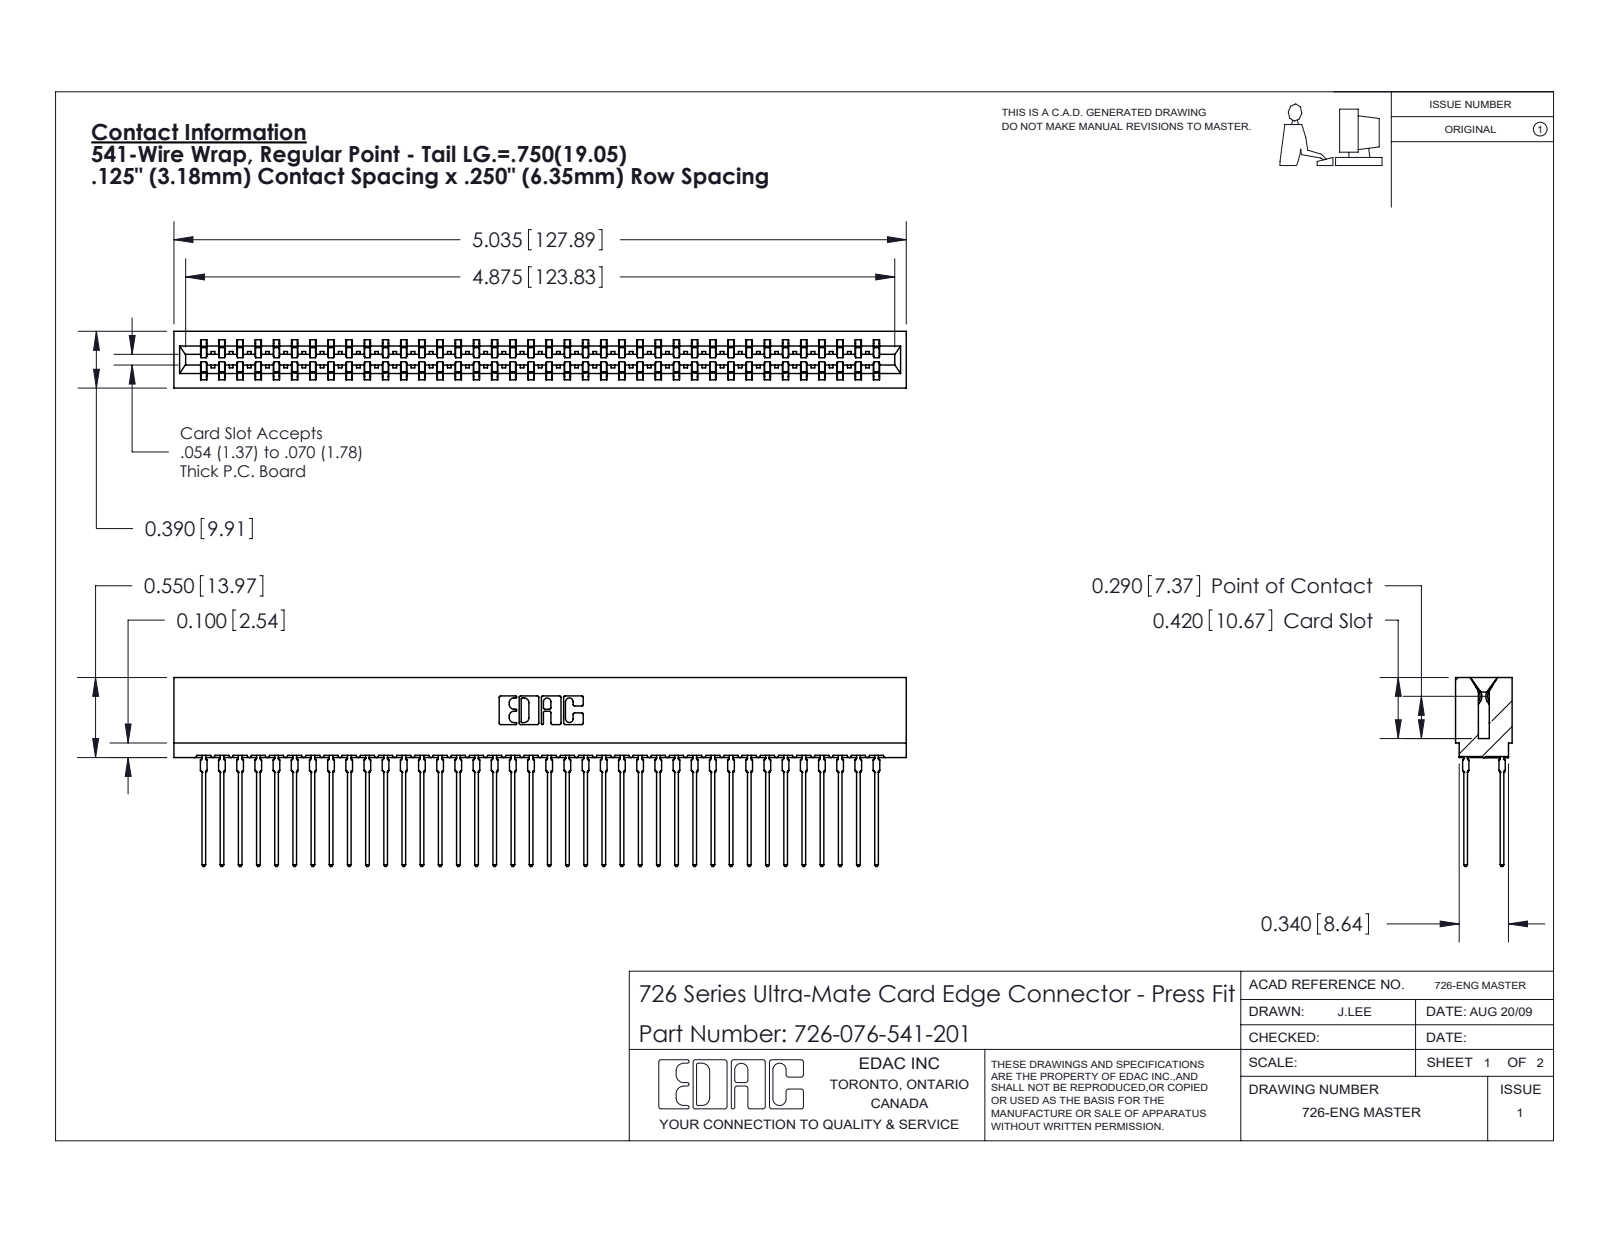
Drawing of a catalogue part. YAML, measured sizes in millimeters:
part_name: "746-292-001_541; 726-076-541-201; 726 Part_.515 Slot Depth - 01"
step_written_by: "SolidWorks 2020 (CONFIG_CONTROL_DESIGN)"
units: millimeters
bodies: {solids: 77, faces: 6899, planar: 3551, cylindrical: 1372, other: 1976}
overall_size: [127.9, 33, 9.9]
volume: 12200
surface_area: 22210
partial_cylinders:
  - {radius: 0.5, count: 152}
  - {radius: 0.4, count: 39}
  - {radius: 0.3, count: 22}
  - {radius: 0.1, count: 8}
  - {radius: 0.3, count: 8}
  - {radius: 0.2, count: 6}
  - {radius: 0.8, count: 6}
  - {radius: 0.7, count: 3}
face_to_face_distances: [1.4, 8.5, 6.4, 0.6, 7.8, 9.9, 2.1, 7, 5.7, 12.7]
